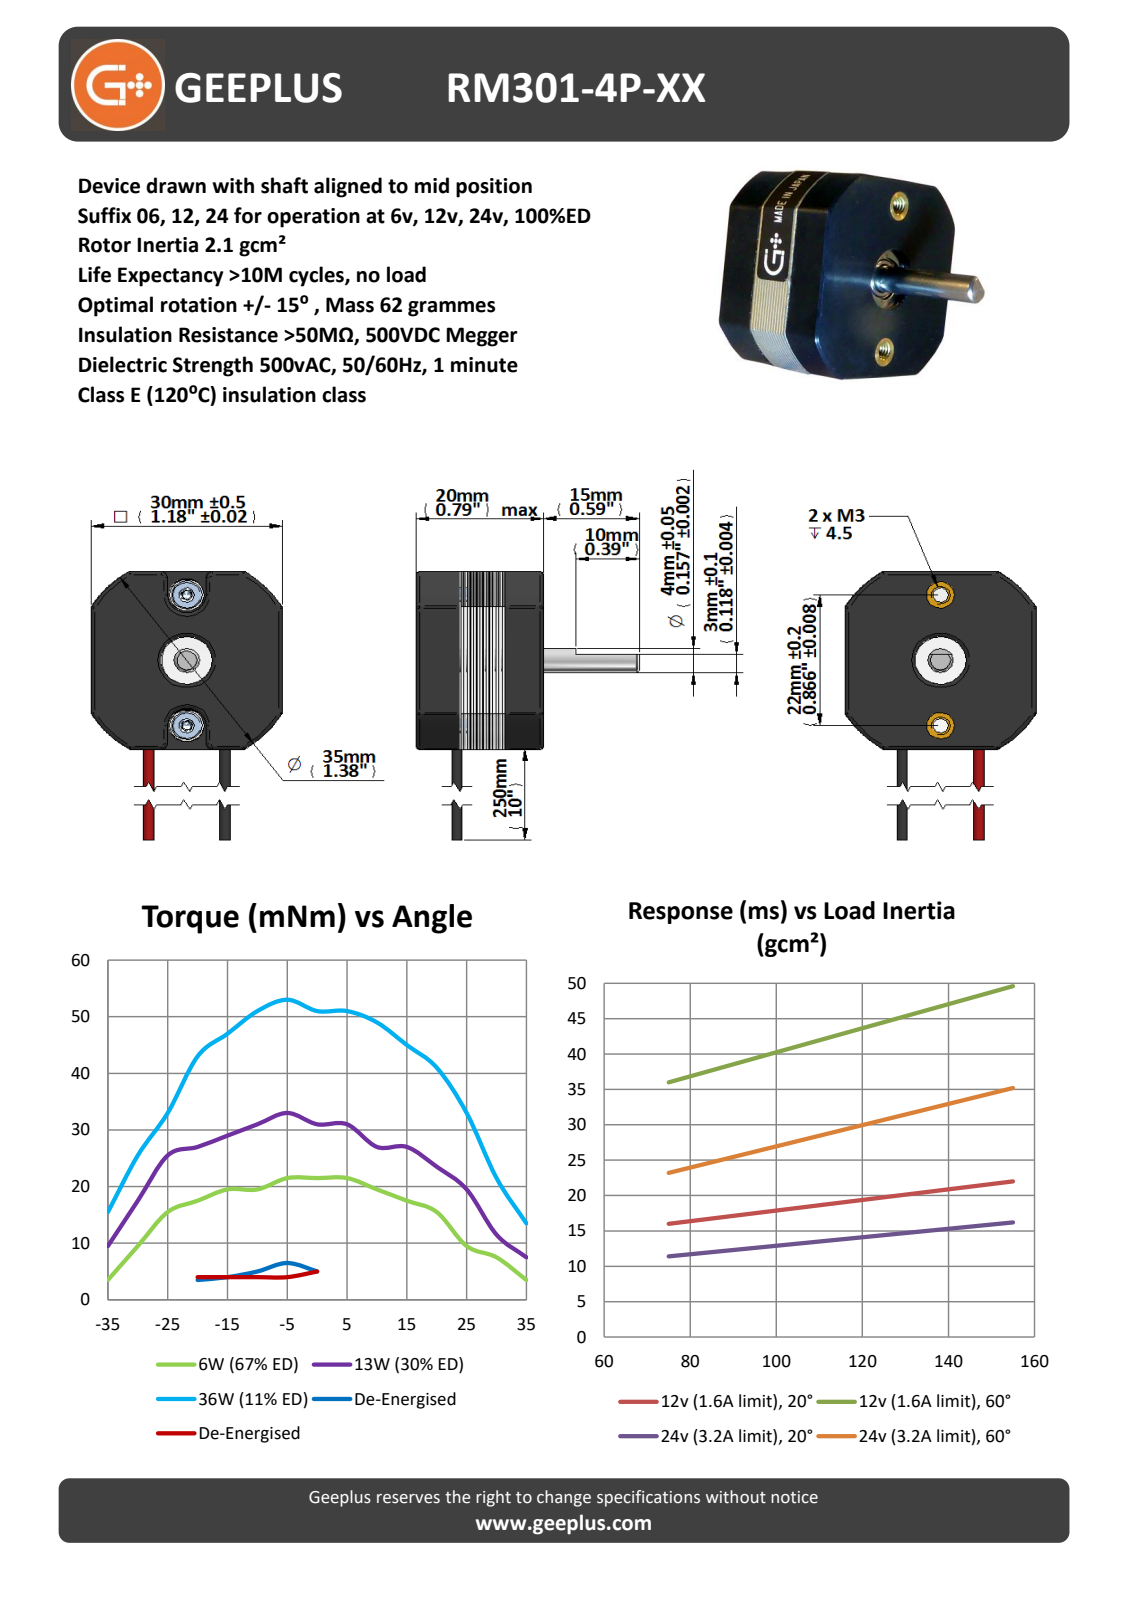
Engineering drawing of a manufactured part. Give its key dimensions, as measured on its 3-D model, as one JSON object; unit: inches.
{"part_name": "RM301-4P-parametric; rm301-4p-rear; rm301-4p-front; rm301-washer (+4 more)", "step_written_by": "Solid Edge (AUTOMOTIVE_DESIGN)", "units": "inches", "bodies": {"solids": 23, "faces": 481, "planar": 160, "cylindrical": 231, "other": 90}, "overall_size": [11.024, 1.378, 1.181], "volume_in3": 1.011, "surface_area_in2": 49.75, "round_holes": [[0.126, 4], [0.055, 2], [0.098, 2], [0.177, 2], [0.315, 1]], "round_bosses_or_shafts": [[0.217, 2], [0.189, 2], [0.063, 2], [0.157, 1]], "partial_cylinders_radius": [[0.008, 48], [0.024, 18], [0.039, 4], [0.118, 2], [0.689, 1]], "face_to_face_distances": [0.02, 0.039, 0.059, 0.079, 0.098, 0.118, 0.138, 0.157, 0.175, 0.156], "hole_center_spacings": [0.433, 0.613, 0.866]}
